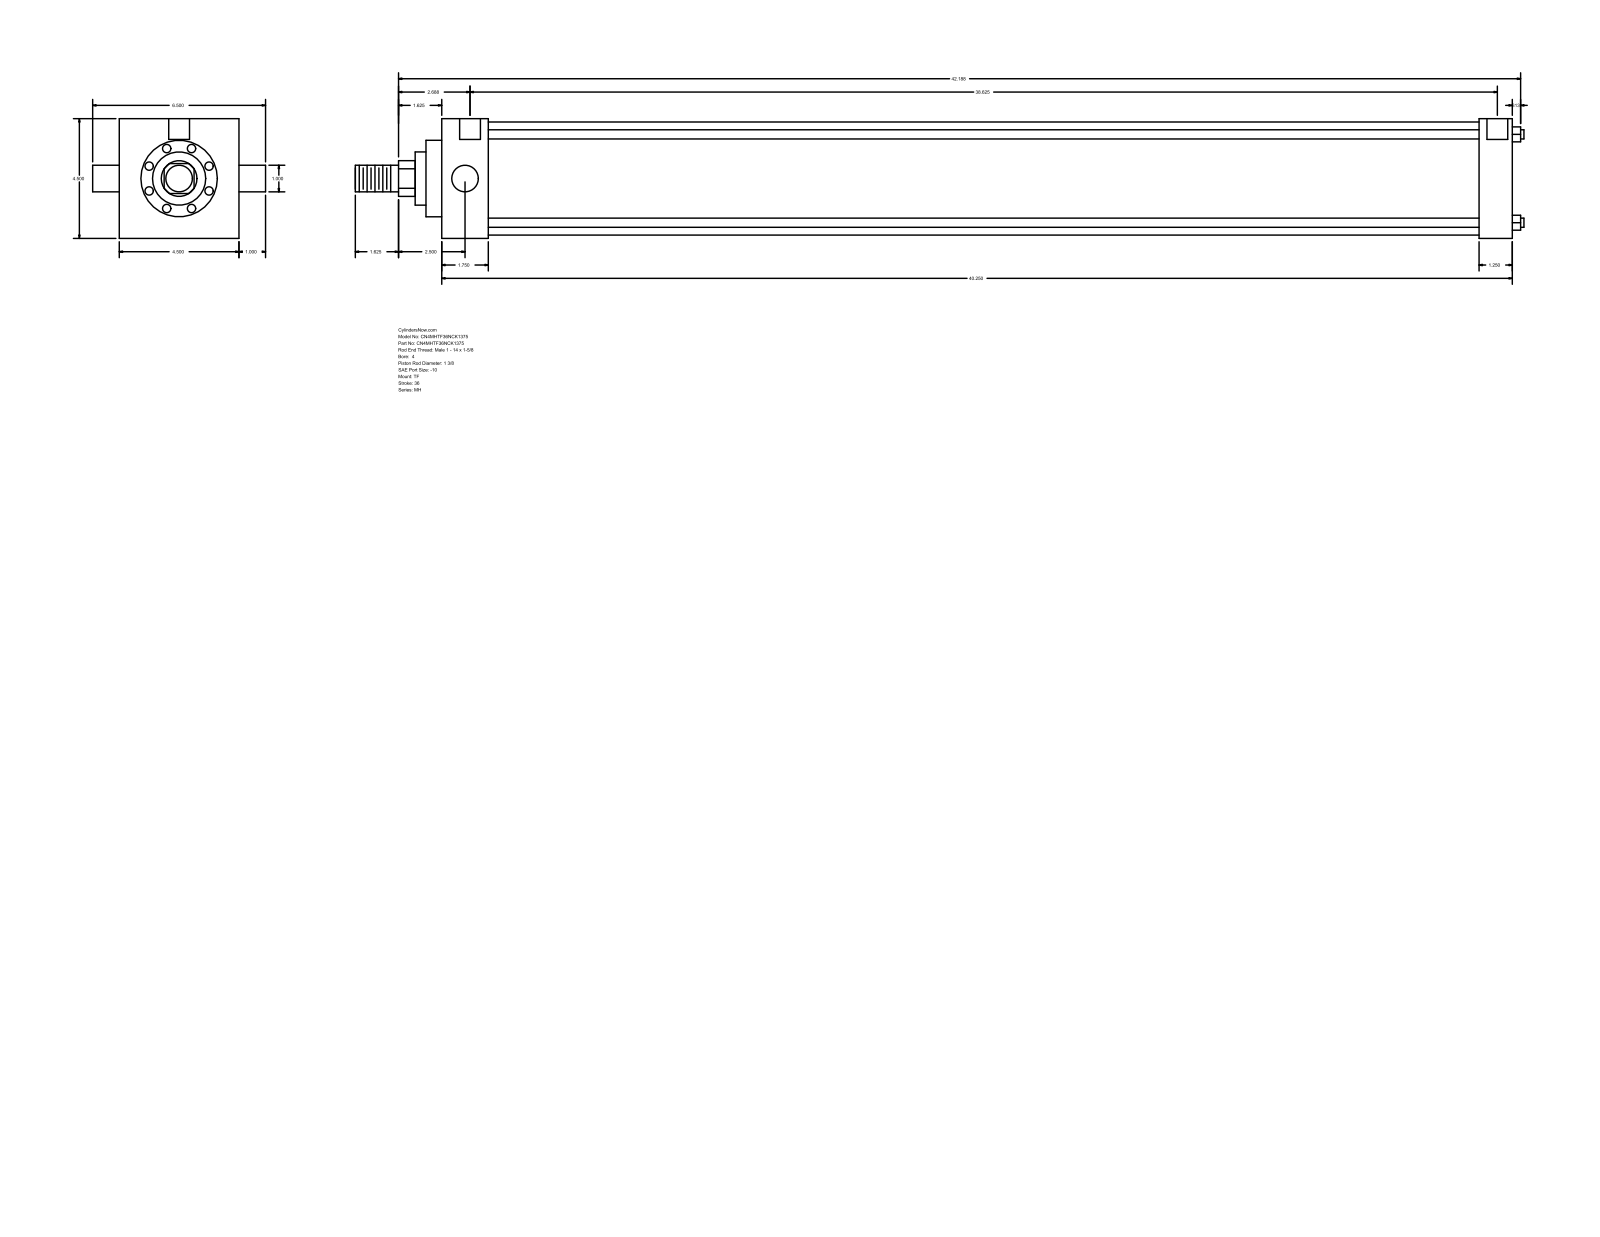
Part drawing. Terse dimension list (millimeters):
name: MH_TF__0400_1.375
written by: GSSL Pune (CONFIG_CONTROL_DESIGN)
unit: mm
bodies: 0 solids, 86 faces (61 planar, 25 cylindrical, 0 other)
size: 1116.01 × 165.1 × 114.3
holes: 3× ⌀8.73, 2× ⌀19.84
bosses: 4× ⌀8.76, 2× ⌀25.4, 1× ⌀107.95, 1× ⌀73.03, 1× ⌀50.8, 1× ⌀34.92
rounds: 1× R17.06
face distances: 114.3, 1022.35, 44.45, 977.9, 990.61, 946.16, 31.74, 15.08, 59.53, 1005.69
hole spacings: 1.58, 1.59, 981.08, 982.66, 982.67, 984.25
